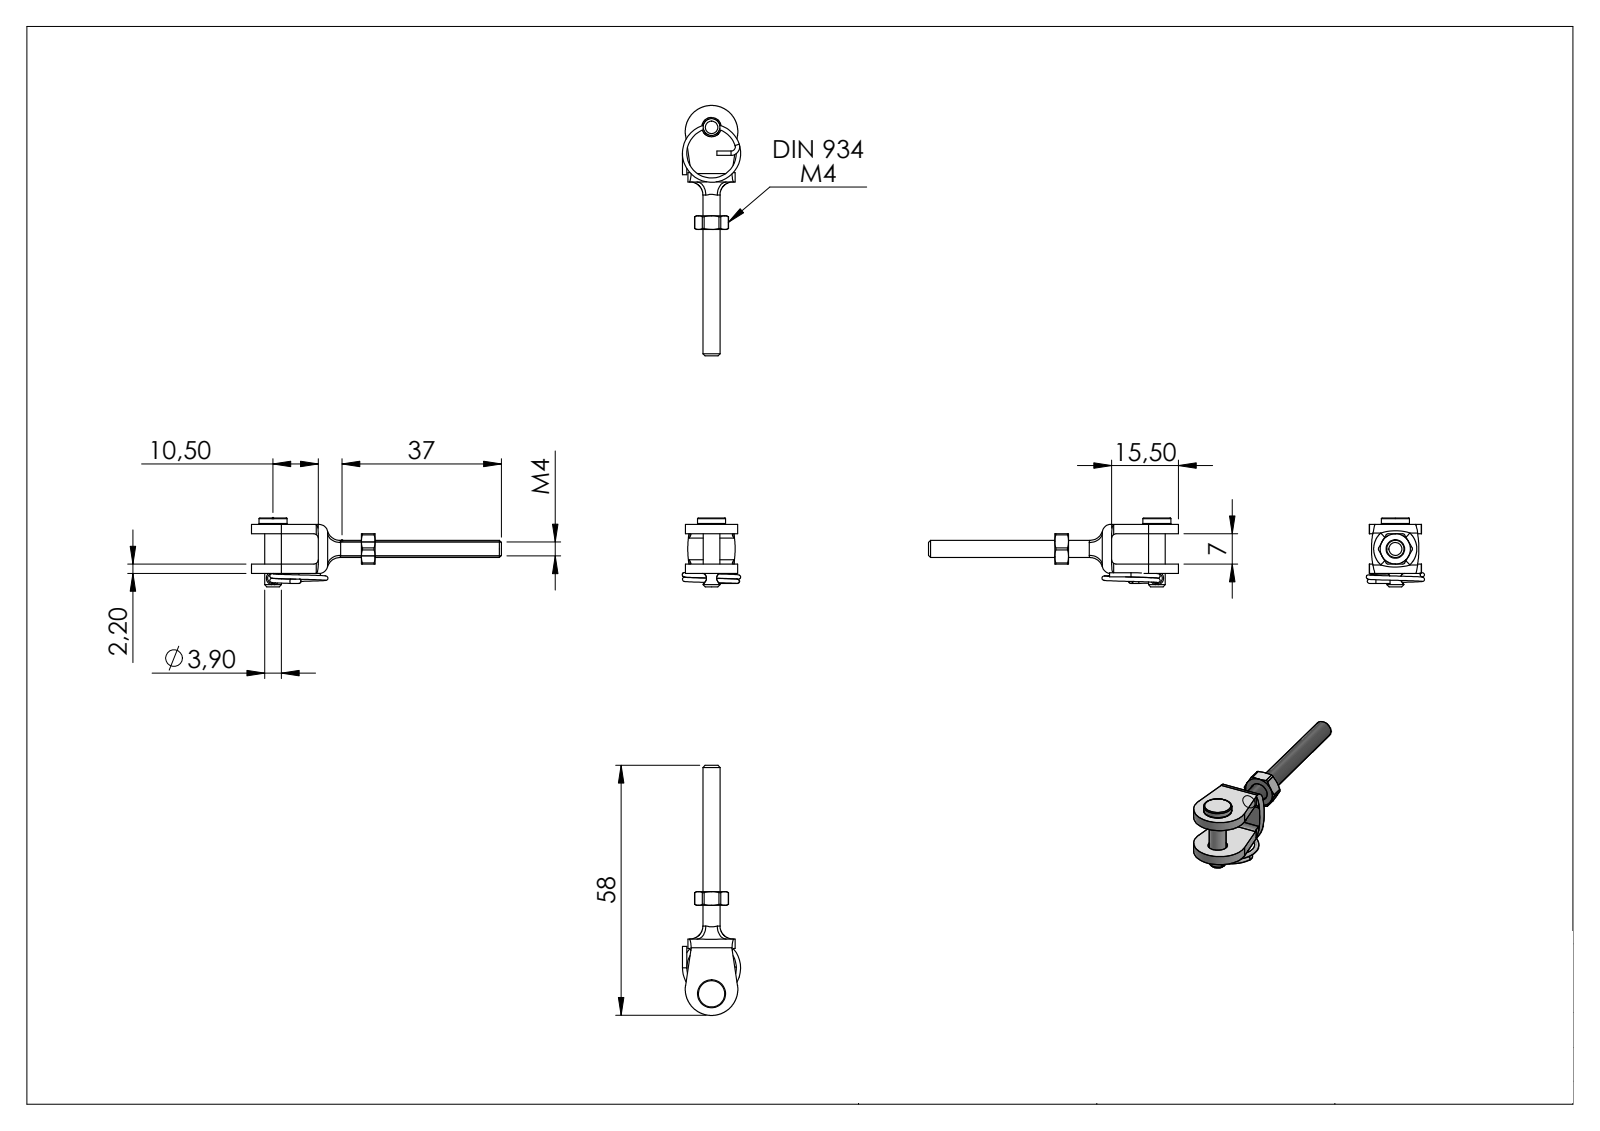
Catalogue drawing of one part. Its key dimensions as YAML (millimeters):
part_name: "100058004; DIN 934 M4-M20_58321-240-4; 10005800X Teil3_100059004 Teil2; 10005800X Teil2_100058004 Teil2 (+1 more)"
step_written_by: "SolidWorks 2015 (CONFIG_CONTROL_DESIGN)"
units: millimeters
bodies: {solids: 4, faces: 327, planar: 132, cylindrical: 38, other: 157}
overall_size: [58, 16, 13.5]
volume: 1783
surface_area: 2228
round_holes:
  - {diameter: 2.5, count: 1}
  - {diameter: 3.3, count: 1}
  - {diameter: 4.5, count: 1}
round_bosses_or_shafts:
  - {diameter: 1, count: 2}
  - {diameter: 6.5, count: 1}
  - {diameter: 4, count: 1}
  - {diameter: 3.9, count: 1}
partial_cylinders:
  - {radius: 0.5, count: 6}
  - {radius: 0.4, count: 2}
  - {radius: 1, count: 2}
  - {radius: 2, count: 2}
  - {radius: 22.04, count: 2}
  - {radius: 6.06, count: 1}
face_to_face_distances: [2.2, 9.2, 7, 11.4, 1.5, 12.9, 10.7, 3.7, 10, 3.2]
